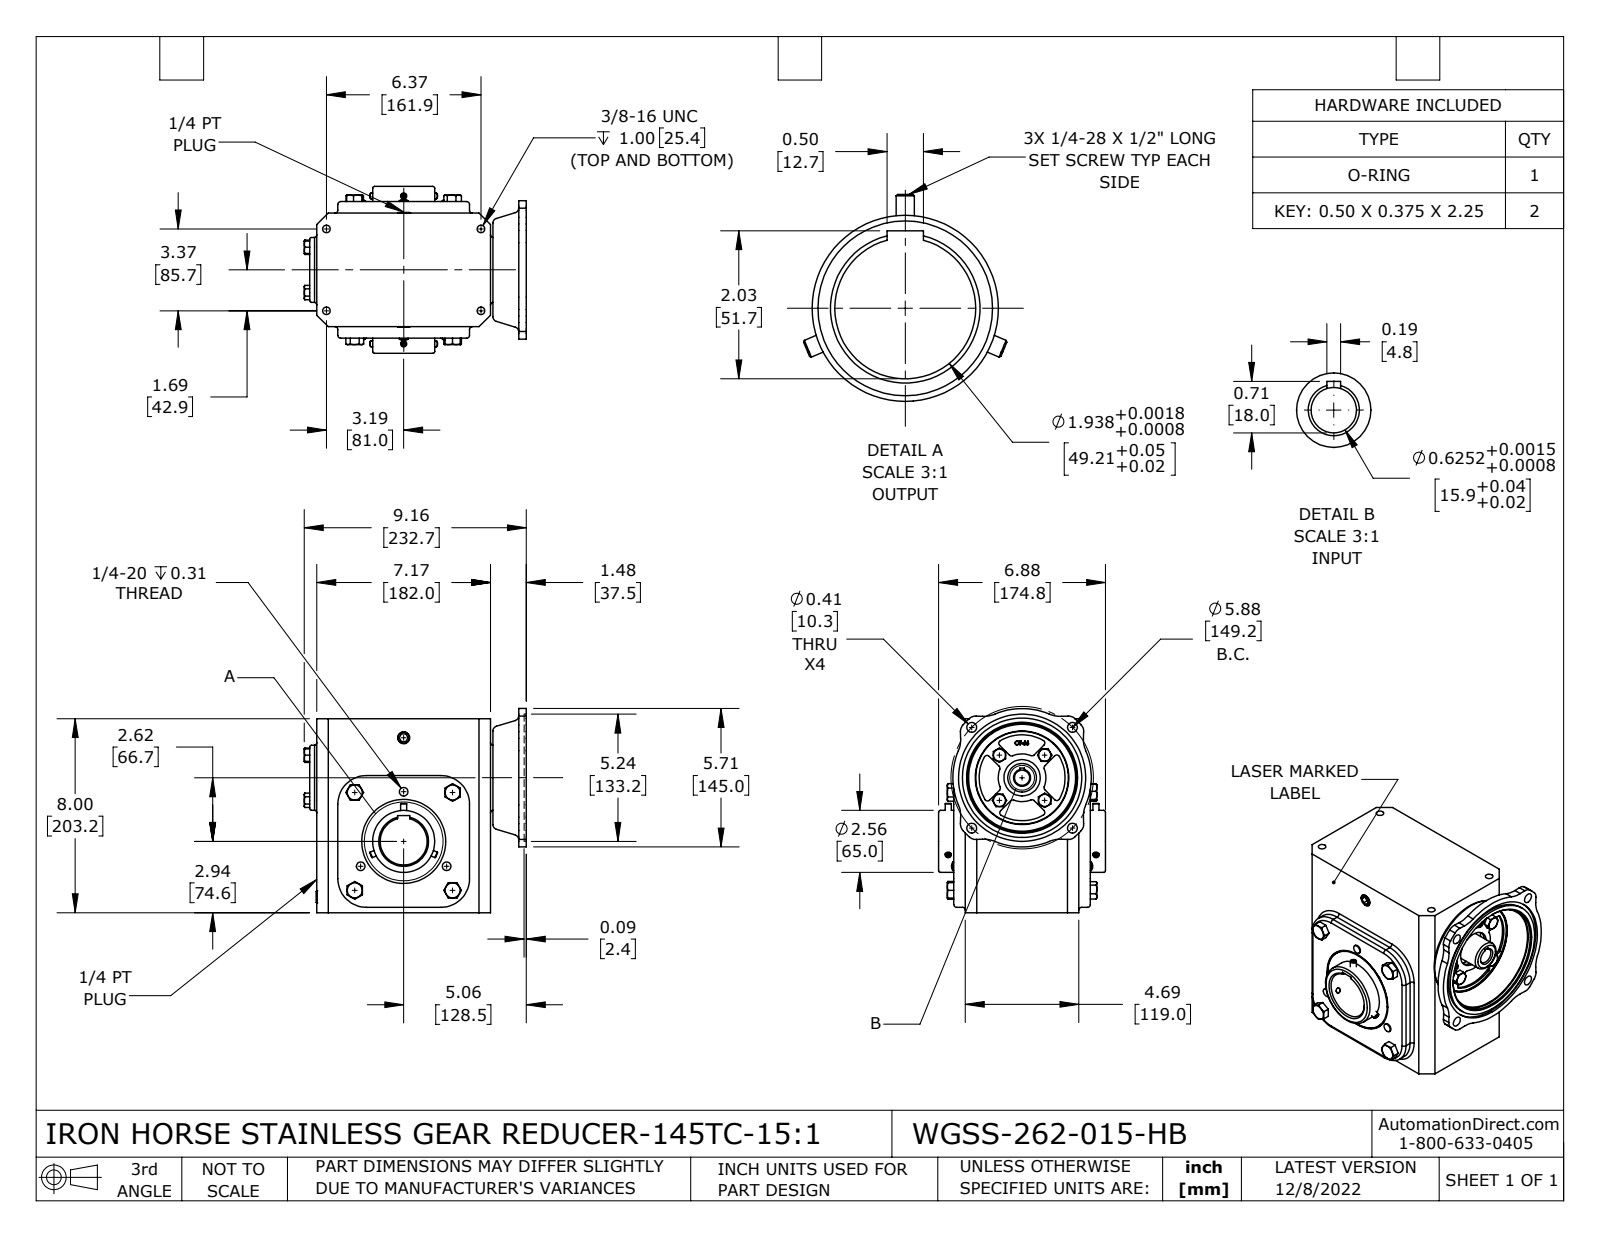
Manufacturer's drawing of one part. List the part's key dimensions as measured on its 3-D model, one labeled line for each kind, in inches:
Part name (STEP PRODUCT): WGSS-262-015-HB
STEP written by: SolidWorks 2021 (CONFIG_CONTROL_DESIGN)
Units: inches
Bodies: 7 solids, 669 faces (285 planar, 191 cylindrical, 193 other)
Overall size (bounding box): 9.16 × 8.417 × 6.882
Volume: 289.1 in³ · Surface area: 423.6 in²
Round holes (diameter × count): ⌀0.213 ×6, ⌀0.313 ×4, ⌀0.406 ×4, ⌀0.625 ×1, ⌀0.866 ×1, ⌀1.496 ×1, ⌀1.772 ×1, ⌀1.937 ×1, ⌀2.047 ×1, ⌀3.819 ×1, ⌀4.5 ×1, ⌀5.244 ×1
Round bosses / shafts (diameter × count): ⌀0.25 ×6, ⌀0.354 ×3, ⌀4.921 ×1, ⌀3.465 ×1, ⌀2.559 ×1, ⌀1.181 ×1
Partial cylindrical surfaces — rounded edges, fillets, slot ends (radius × count): R0.118 ×40, R0.394 ×12, R1.181 ×12, R0.079 ×4, R0.984 ×1, R1.772 ×1, R2.854 ×1, R3.27 ×1
Main face-to-face distances: 0.472, 5.157, 8, 7.165, 4.685, 5.63, 7.461, 7.71, 0.295, 1.161
Hole centre spacings: 2.937, 3.465, 4.154, 5.707, 6.094, 3.375, 5.875, 6.375
